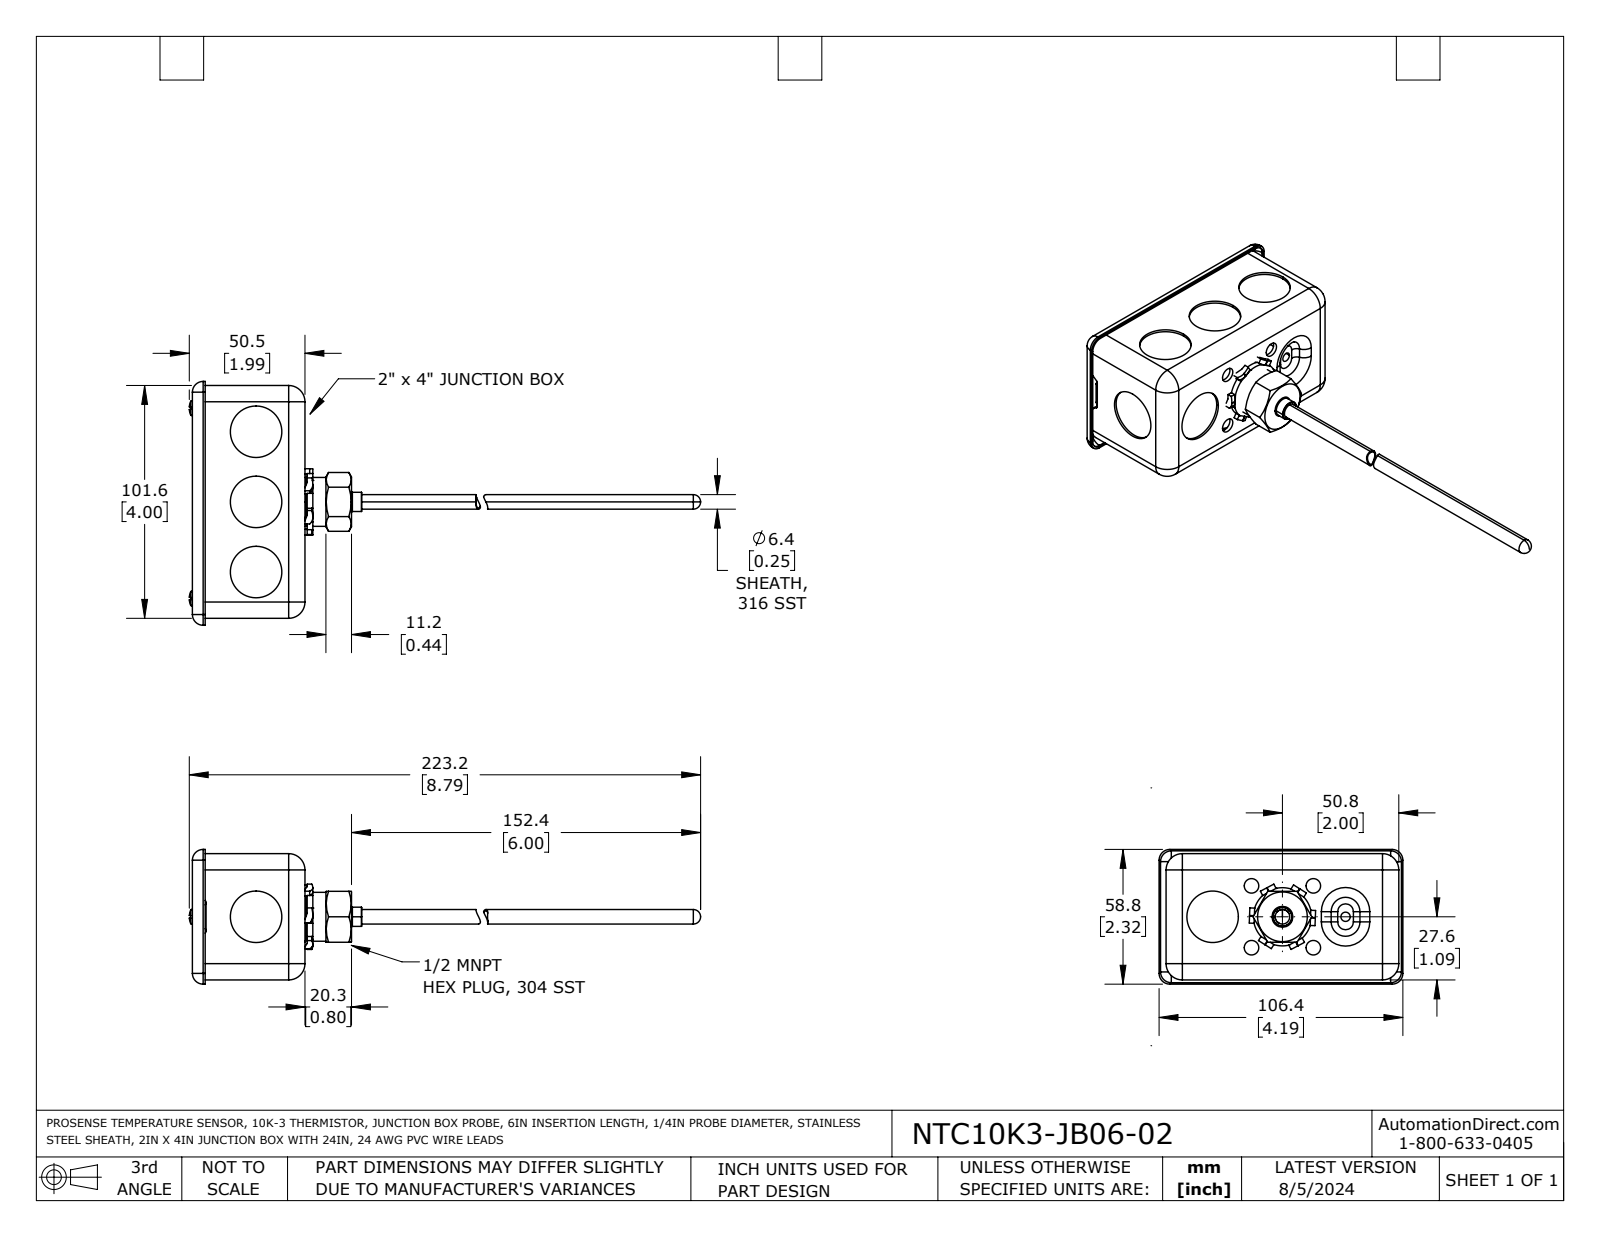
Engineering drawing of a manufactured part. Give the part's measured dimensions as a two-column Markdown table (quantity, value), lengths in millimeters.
| quantity | value |
| --- | --- |
| part name | NTC10K3-JB06-02 |
| STEP written by | SolidWorks 2021 (AUTOMOTIVE_DESIGN) |
| units | millimeters |
| bodies | 5 solids, 358 faces (153 planar, 143 cylindrical, 62 other) |
| overall size | 223.2 × 106.4 × 58.8 |
| volume | 46 110 mm³ |
| surface area | 63 630 mm² |
| round holes (diameter × count) | 22.5 × 6, 6.4 × 4, 2.9 × 2, 4.1 × 1, 5.3 × 1, 6.4 × 1, 11.1 × 1 |
| round bosses / shafts (diameter × count) | 3.5 × 2, 21.3 × 1, 8.4 × 1, 6.4 × 1 |
| partial cylindrical surfaces (radius × count) | 4.7 × 16, 6.2 × 8, 7.1 × 8, 4.4 × 6, 14.1 × 6, 1.1 × 4, 4.2 × 4, 1.8 × 2 |
| main face-to-face distances | 1.8, 0.8, 51.6, 53.3, 1, 2.5, 1.5, 47.1, 52.6, 54.1 |
| hole center spacings | 19.1, 27, 31.7, 57.3, 19.5, 21.7, 30.6, 38.2 |
